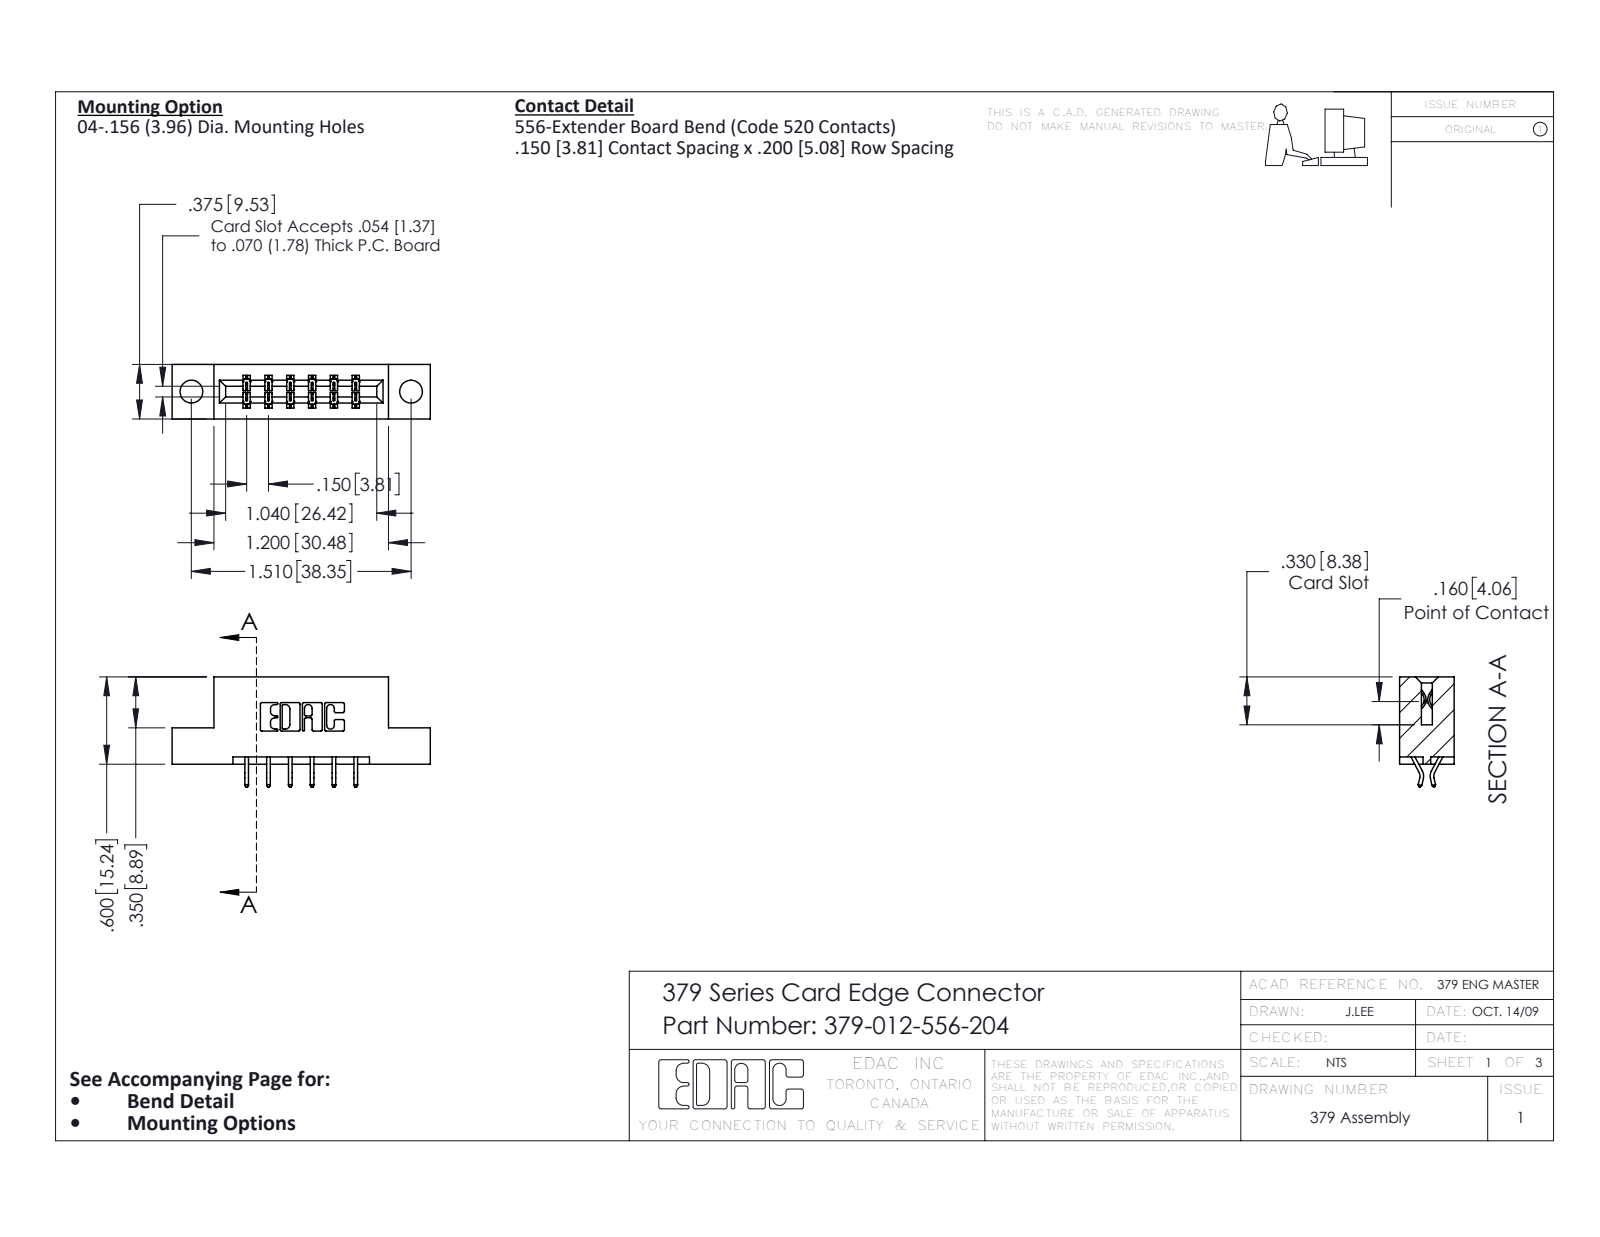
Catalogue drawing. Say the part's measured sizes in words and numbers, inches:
The part is named "379-012-556-204; 379 Part_Flush - .156 Dia - TH; 345-292-001_556 Tail". Its 3-D file was written by "SolidWorks 2016 (CONFIG_CONTROL_DESIGN)". It is 13 solids with 810 faces: 550 planar, 260 cylindrical and 0 other. Overall it measures 1.775 by 0.757 by 0.375 inches. Its volume is 0.26 cubic inches and its surface area 6.567 square inches. Round holes: 2 of diameter 0.156. Partial cylindrical surfaces (rounded edges, fillets, slot ends): 22 of radius 0.01, 18 of radius 0.006, 6 of radius 0.007, 6 of radius 0.031, 3 of radius 0.026, 2 of radius 0.01, 2 of radius 0.014, 2 of radius 0.022. The main face-to-face distances are 0.3, 0.2, 0.05, 0.15, 0.375, 0.25, 0.35, 0.1, 0.075, 0.55. The hole center spacings are 1.51.
